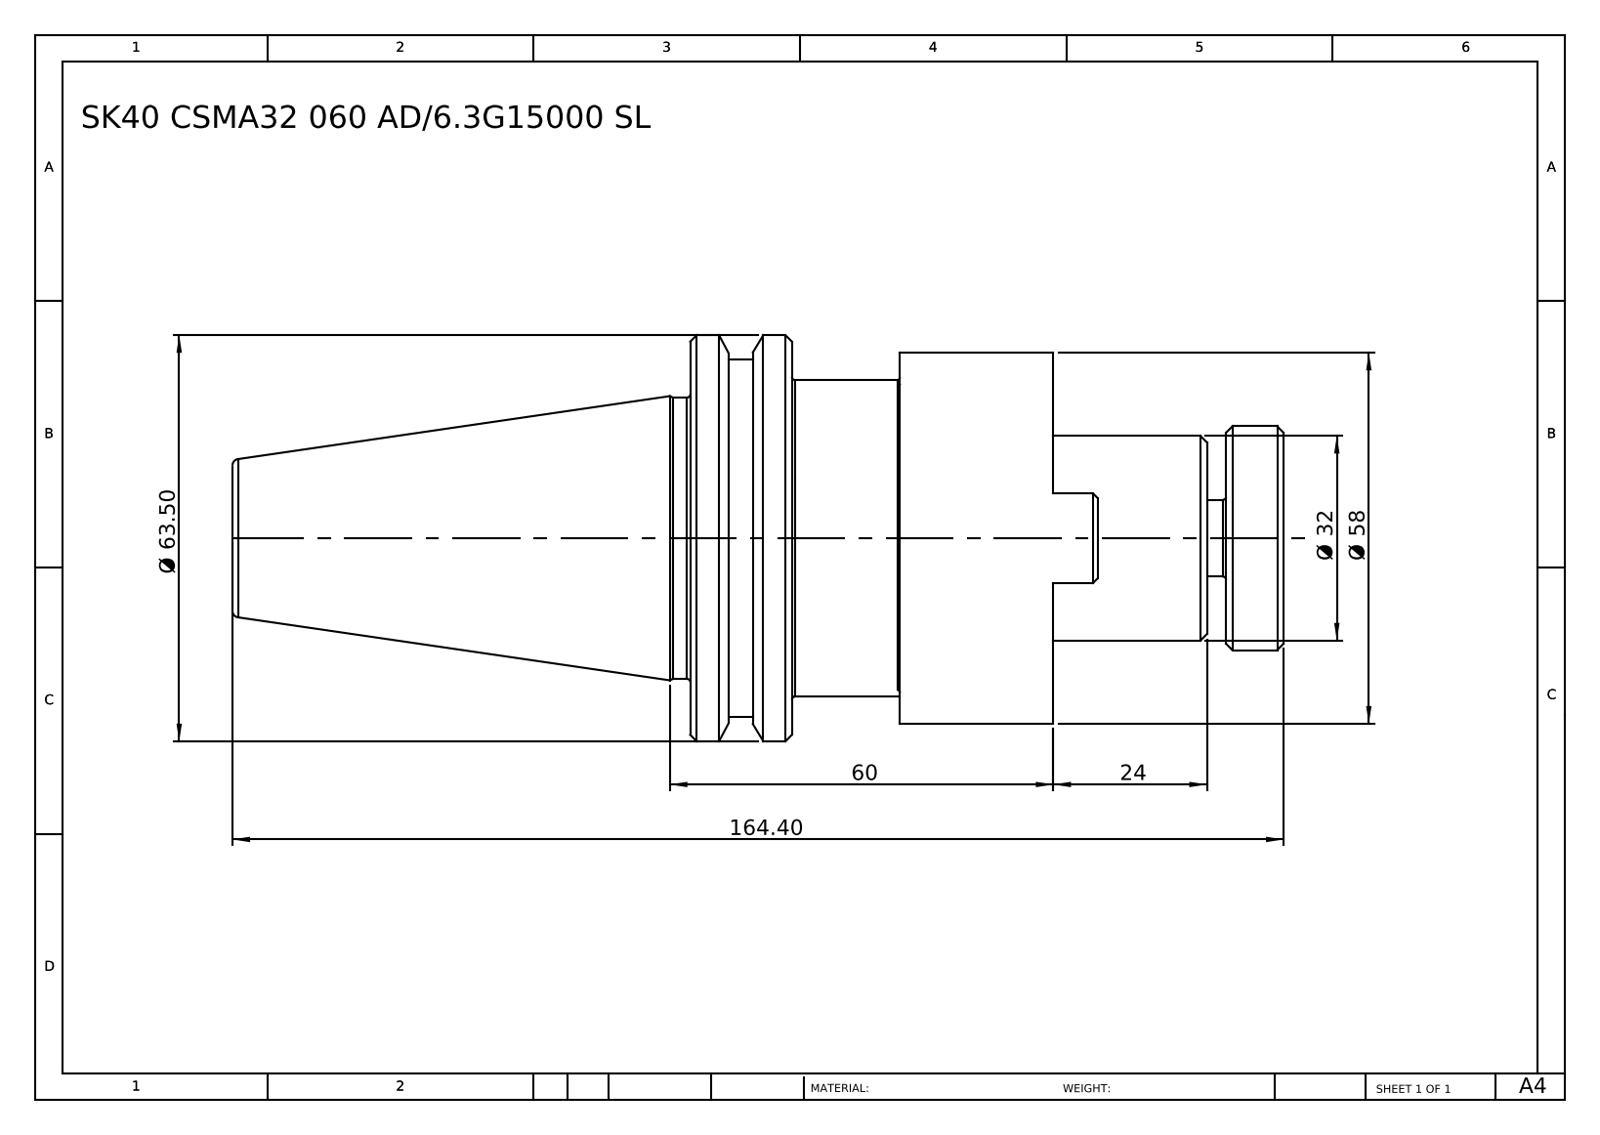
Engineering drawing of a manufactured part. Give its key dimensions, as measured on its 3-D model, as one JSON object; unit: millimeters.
{"part_name": "SK 40 CSMA32 060 AD-6.3G15000 SL SP.S", "step_written_by": "SolidWorks 2014 (CONFIG_CONTROL_DESIGN)", "units": "millimeters", "bodies": {"solids": 1, "faces": 78, "planar": 20, "cylindrical": 20, "other": 38}, "overall_size": [164.4, 63.65, 63.65], "volume_mm3": 243428, "surface_area_mm2": 31034, "round_bosses_or_shafts": [[63.5, 1], [58, 1], [56, 1], [49.5, 1], [44, 1], [35, 1], [32, 1], [12, 1]], "partial_cylinders_radius": [[7, 1], [18, 1]], "face_to_face_distances": [56.8, 24, 40.9, 15.9, 36, 76.9, 92.8, 9, 27, 67.9]}
